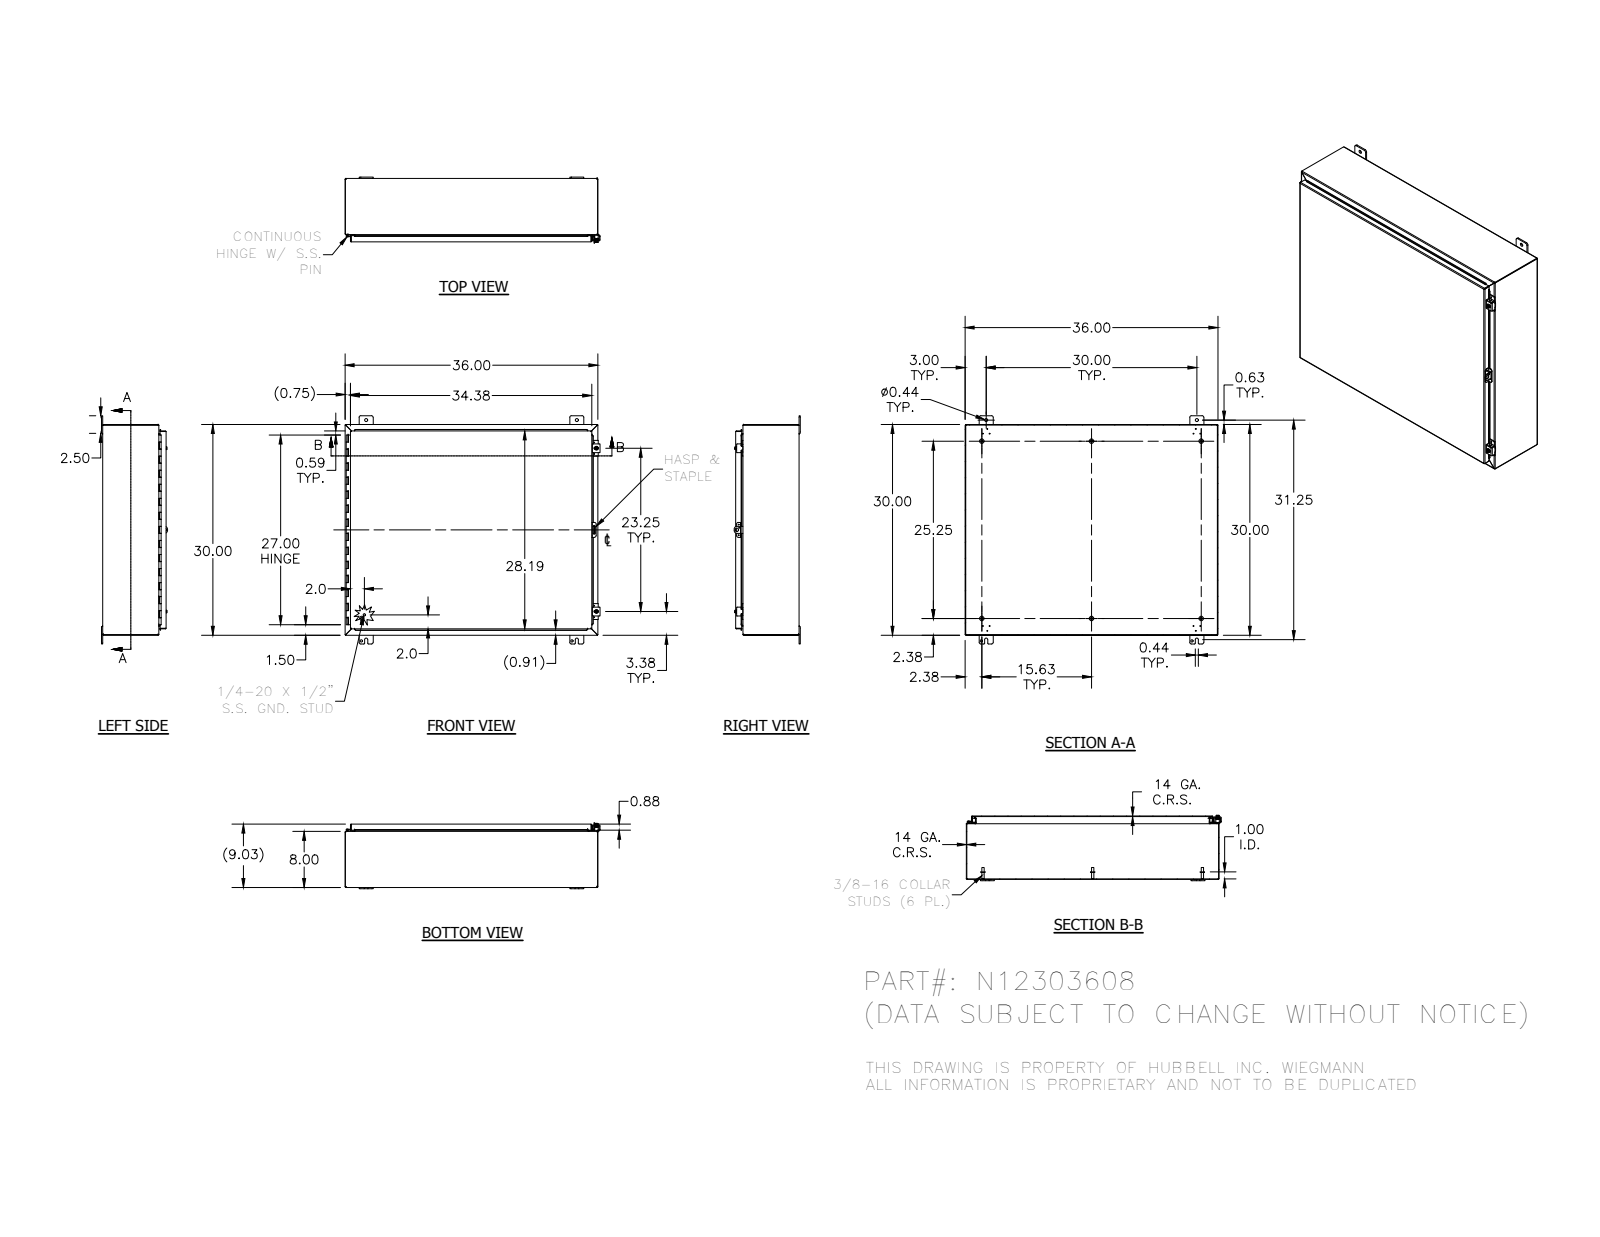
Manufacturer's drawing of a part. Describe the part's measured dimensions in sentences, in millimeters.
The part is named "N12303608; 34840; 38420; N12303608BKP (+8 more)". Its 3-D file was written by "Autodesk Inventor 2012 (AUTOMOTIVE_DESIGN)". It is 29 solids with 1049 faces: 574 planar, 356 cylindrical and 119 other. Overall it measures 922.3 by 825.5 by 239 millimeters. Its volume is 4 592 000 cubic millimeters and its surface area 4 752 000 square millimeters. Round holes: 12 of diameter 3, 7 of diameter 2.8, 4 of diameter 8, 4 of diameter 11.1, 2 of diameter 5.4, 2 of diameter 7.1, 2 of diameter 7.6, 1 of diameter 3.2, 1 of diameter 4, 1 of diameter 12.7. Round bosses or shafts: 6 of diameter 15.9, 6 of diameter 8.4, 4 of diameter 6.4, 2 of diameter 13.2, 2 of diameter 12.7, 2 of diameter 8.9, 2 of diameter 2.9, 1 of diameter 8.6. Partial cylindrical surfaces (rounded edges, fillets, slot ends): 27 of radius 0.8, 25 of radius 1.6, 25 of radius 3.2, 25 of radius 6.4, 23 of radius 0.8, 23 of radius 2.7, 8 of radius 1.8, 4 of radius 2.5. The main face-to-face distances are 1.9, 227.6, 225.7, 229.4, 760.1, 912.5, 201.3, 26.2, 762, 758.2. The hole center spacings are 762, 19.3, 21.3, 23.9, 24.6, 40.5, 50.7, 695.5.
